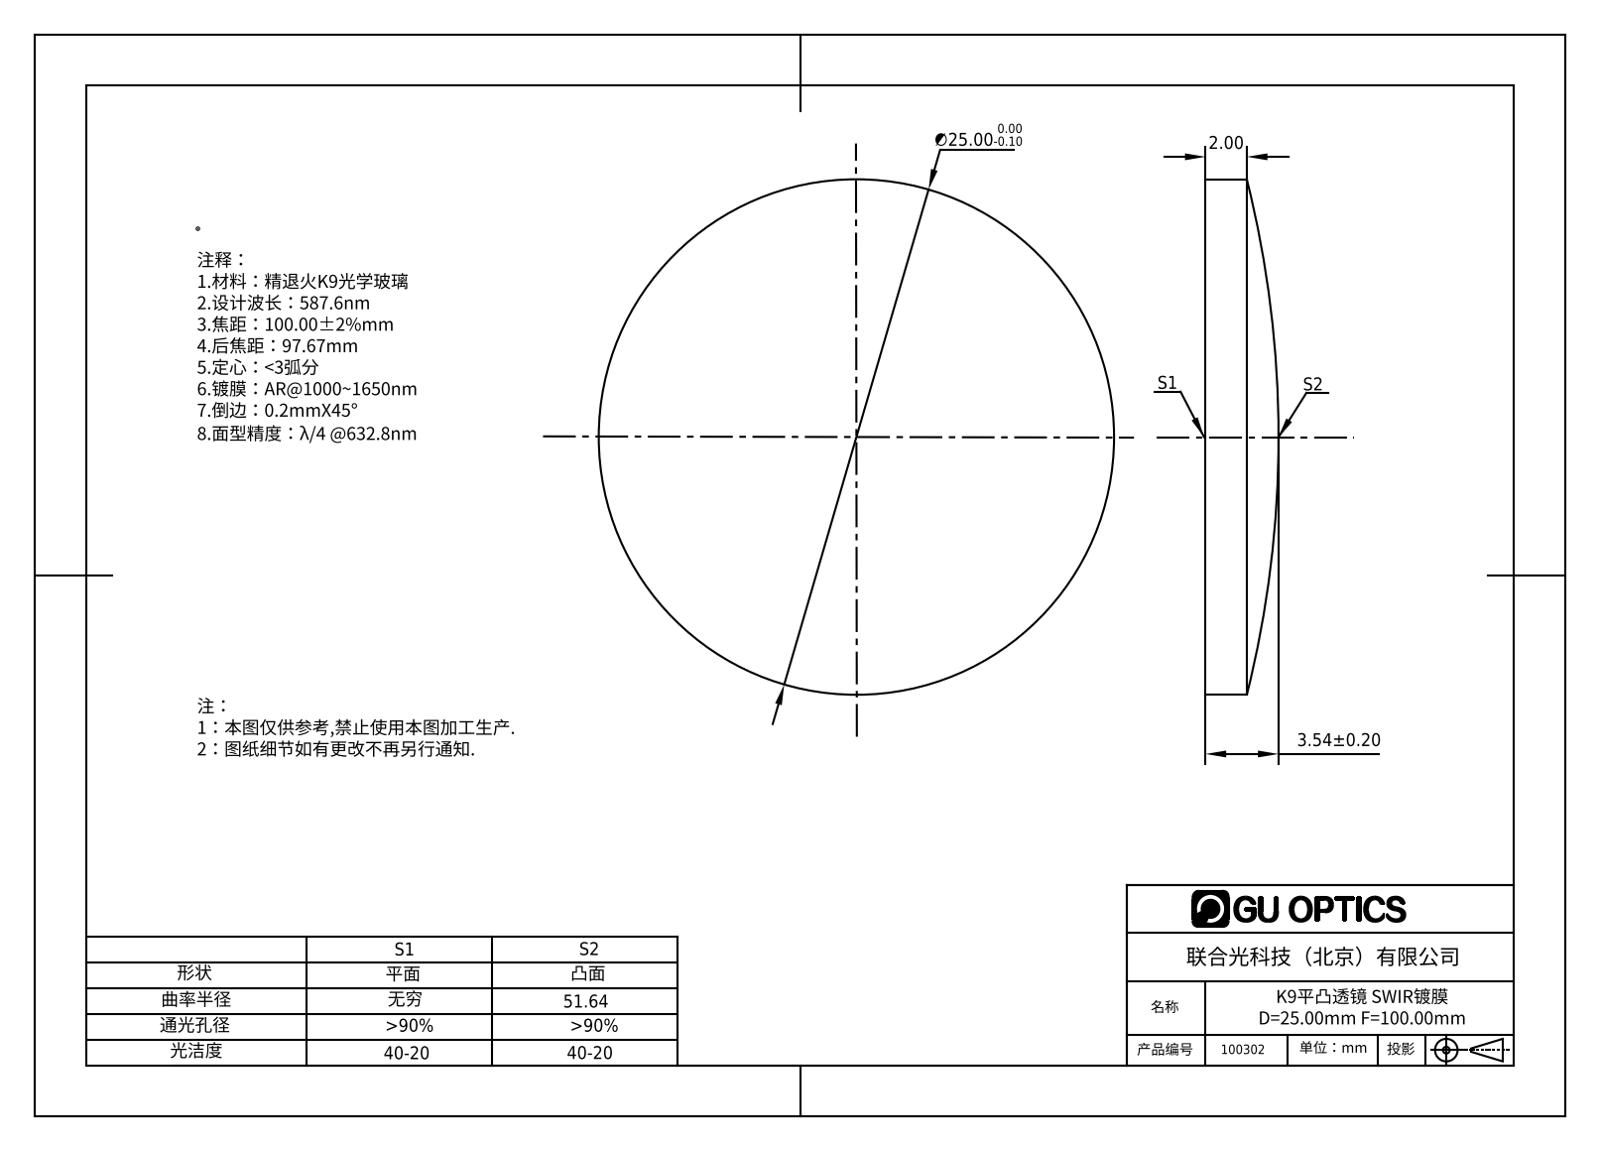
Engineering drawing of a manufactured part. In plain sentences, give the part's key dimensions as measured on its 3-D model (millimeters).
The part is named "100130". Its 3-D file was written by "SolidWorks 2016 (AUTOMOTIVE_DESIGN)". It is 1 solid with 5 faces: 1 planar, 2 cylindrical and 2 other. Overall it measures 25 by 25 by 3.54 millimeters. Its volume is 1 362 cubic millimeters and its surface area 1 146 square millimeters. Round bosses or shafts: 1 of diameter 25.
